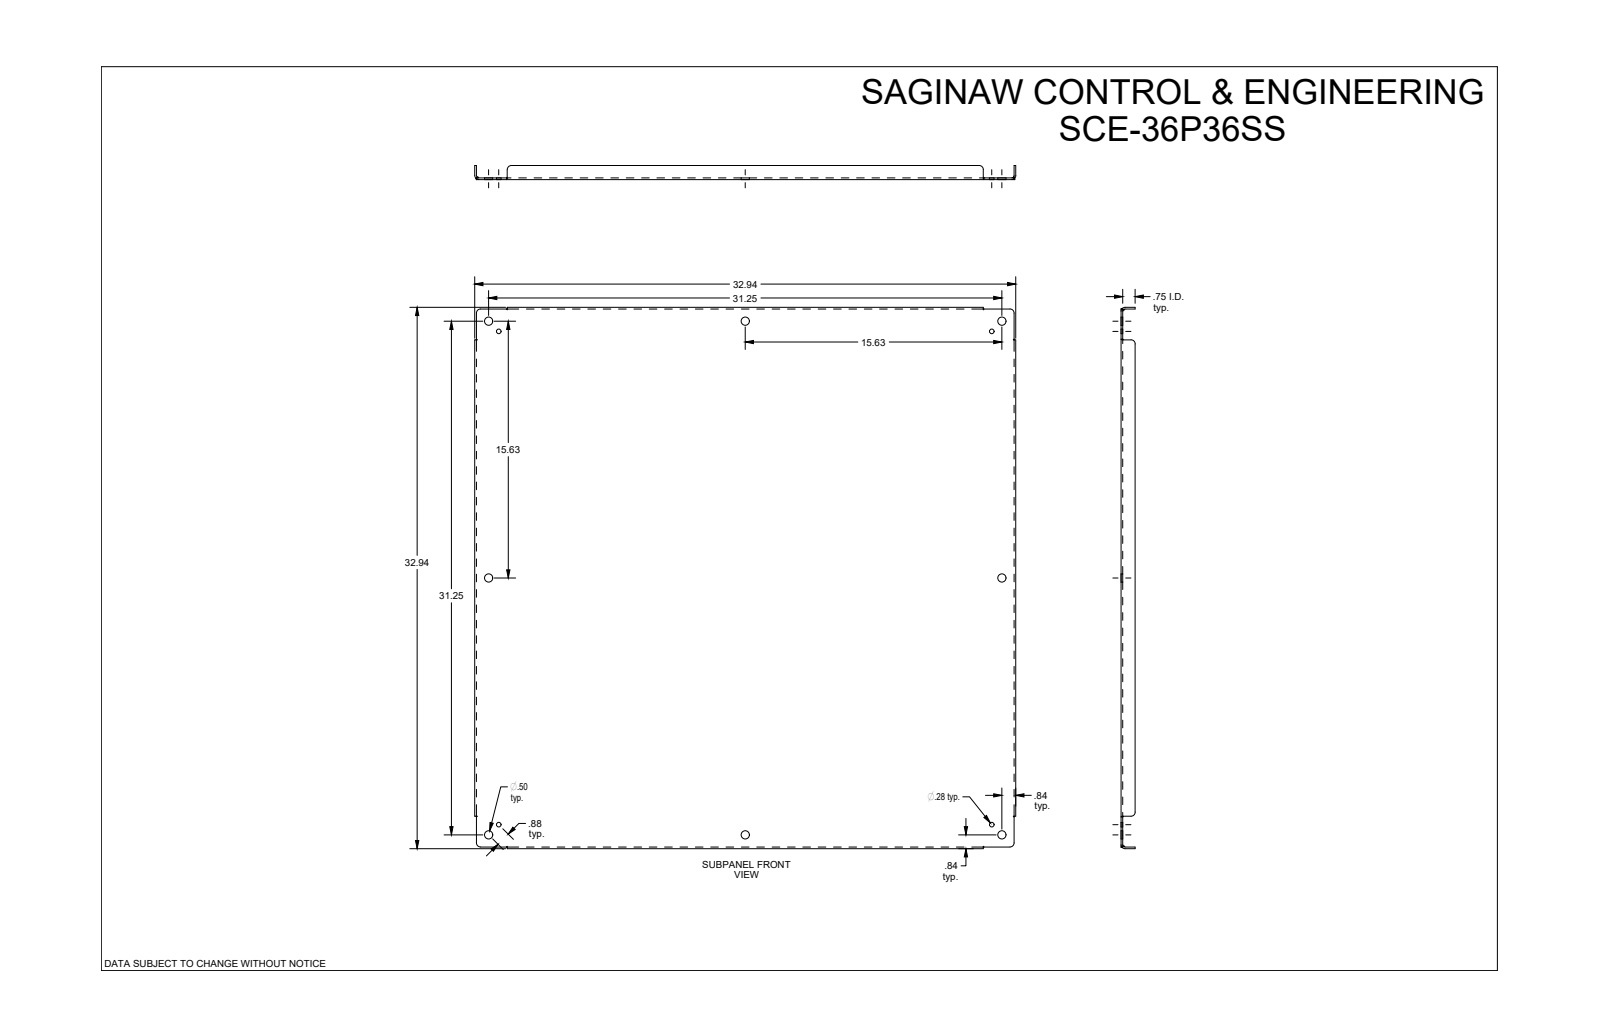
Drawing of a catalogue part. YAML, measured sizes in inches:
part_name: "SCE-36P36SS"
step_written_by: "SolidWorks 2019 (CONFIG_CONTROL_DESIGN)"
units: inches
bodies: {solids: 1, faces: 86, planar: 30, cylindrical: 32, other: 24}
overall_size: [32.941, 32.941, 0.858]
volume: 120.6
surface_area: 2334
round_holes:
  - {diameter: 0.5, count: 8}
  - {diameter: 0.281, count: 4}
partial_cylinders:
  - {radius: 0.25, count: 8}
  - {radius: 0.246, count: 4}
  - {radius: 0.142, count: 2}
  - {radius: 0.143, count: 2}
face_to_face_distances: [0.104, 32.838, 32.734, 32.942, 0.754, 0.858, 1.979, 30.963, 1.875, 30.859]
hole_center_spacings: [15.02, 15.626, 30.639, 34.111, 34.941, 31.252, 0.875, 22.098]
